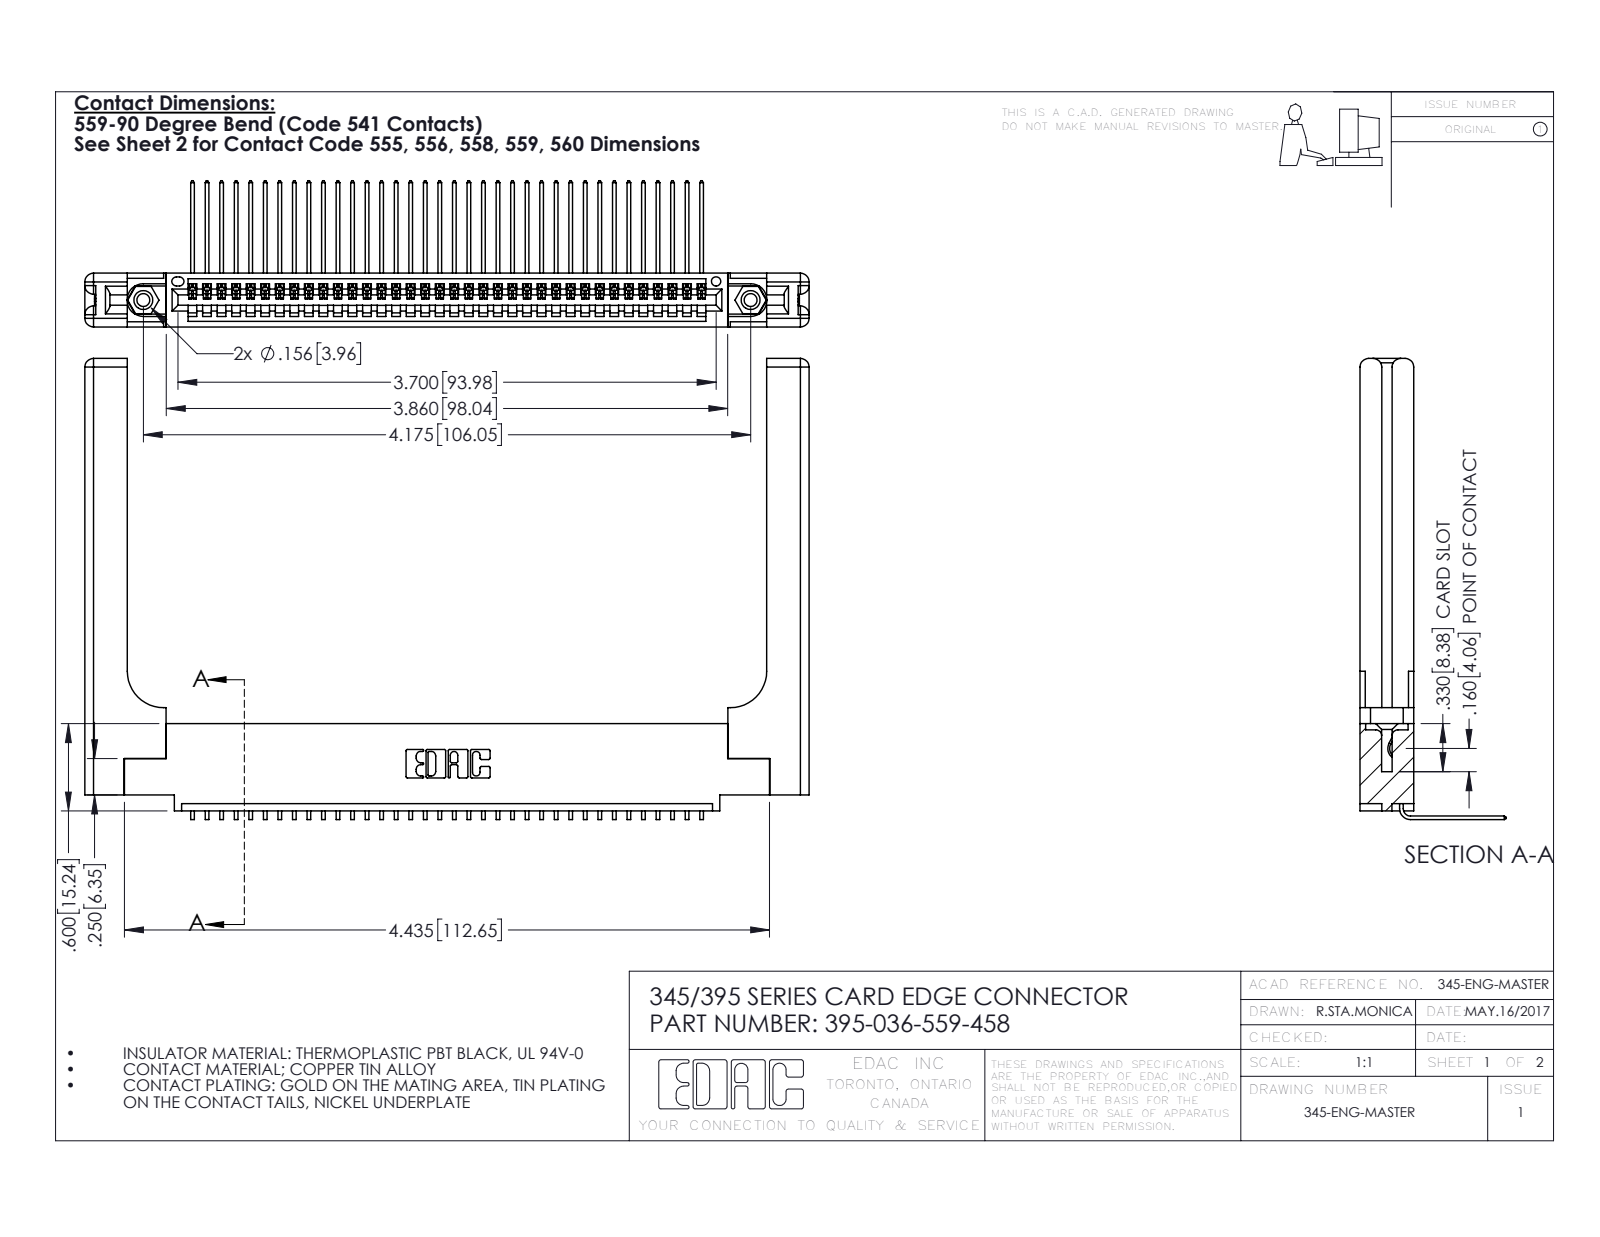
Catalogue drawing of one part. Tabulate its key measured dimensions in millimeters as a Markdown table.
| quantity | value |
| --- | --- |
| part name | 345-250-001_345-250-001-102; 345-292-001_558 559 Tail - 1; 345 Part_0.110 Offset - 0.156 Dia-TH; 395-036-559-458 (+1 more) |
| STEP written by | SolidWorks 2016 (CONFIG_CONTROL_DESIGN) |
| units | millimeters |
| bodies | 41 solids, 2546 faces (1744 planar, 742 cylindrical, 60 other) |
| overall size | 126.5 × 80.5 × 25.5 |
| volume | 20 520 mm³ |
| surface area | 21 970 mm² |
| round holes (diameter × count) | 2.3 × 2, 3.2 × 2, 4 × 2, 1.6 × 1 |
| round bosses / shafts (diameter × count) | 3.9 × 2 |
| partial cylindrical surfaces (radius × count) | 0.2 × 72, 0.3 × 22, 1.5 × 16, 0.2 × 6, 0.8 × 6, 0.7 × 3, 0.8 × 2, 0.8 × 2 |
| main face-to-face distances | 9.4, 1.8, 7.6, 5.1, 2.5, 6.9, 0.6, 3.8, 3.8, 5.7 |
| hole center spacings | 6.9, 100.1, 106 |
